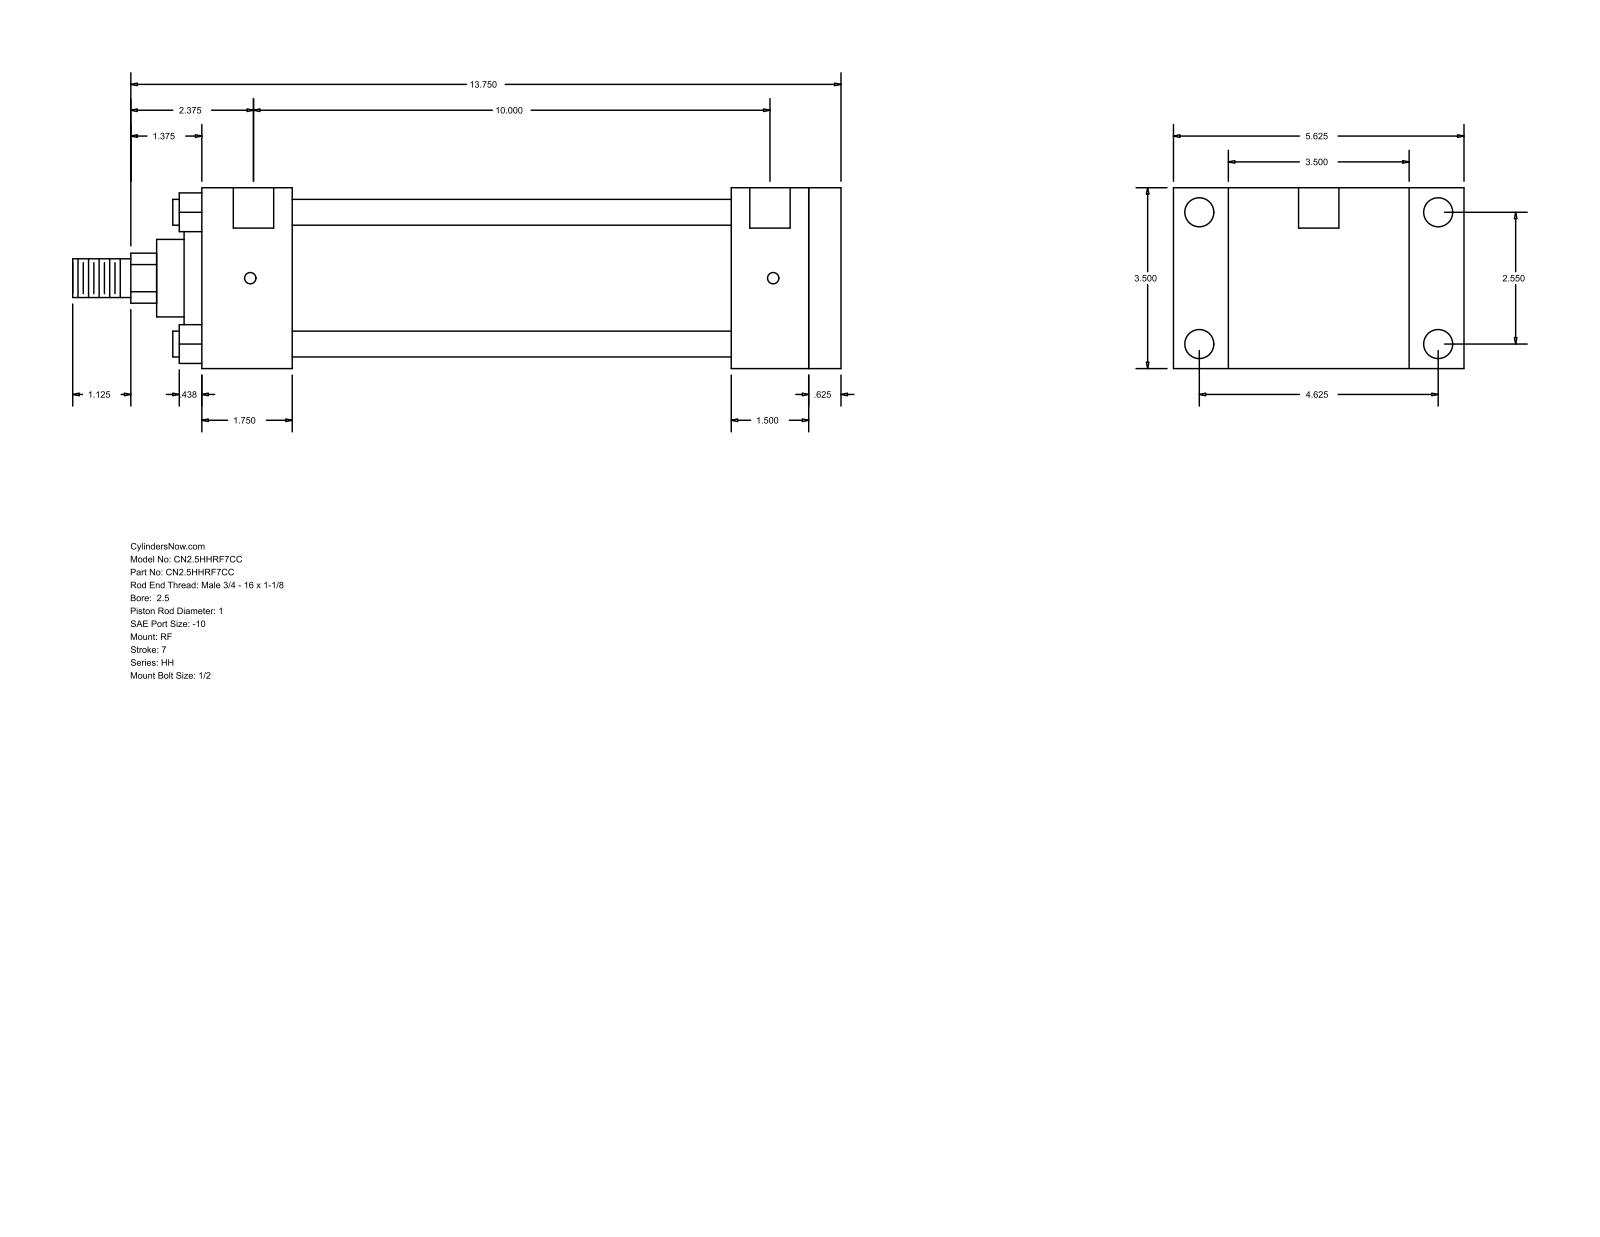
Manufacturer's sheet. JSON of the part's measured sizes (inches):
{"part_name": "HH_RF__0250_1", "step_written_by": "GSSL Pune (CONFIG_CONTROL_DESIGN)", "units": "inches", "bodies": {"solids": 0, "faces": 94, "planar": 65, "cylindrical": 29, "other": 0}, "overall_size": [14.875, 5.625, 3.5], "round_holes": [[0.219, 4], [0.563, 4], [0.781, 2]], "round_bosses_or_shafts": [[0.5, 4], [2.875, 1], [2.375, 1], [1.5, 1], [1, 1], [0.75, 1]], "partial_cylinders_radius": [[0.484, 1]], "face_to_face_distances": [3.5, 0.625, 11.75, 12.375, 1.75, 10, 10.625, 10.25, 8.5, 1.5], "hole_center_spacings": [0.063, 2.55, 4.625, 5.281, 10.062, 10.125, 10]}
